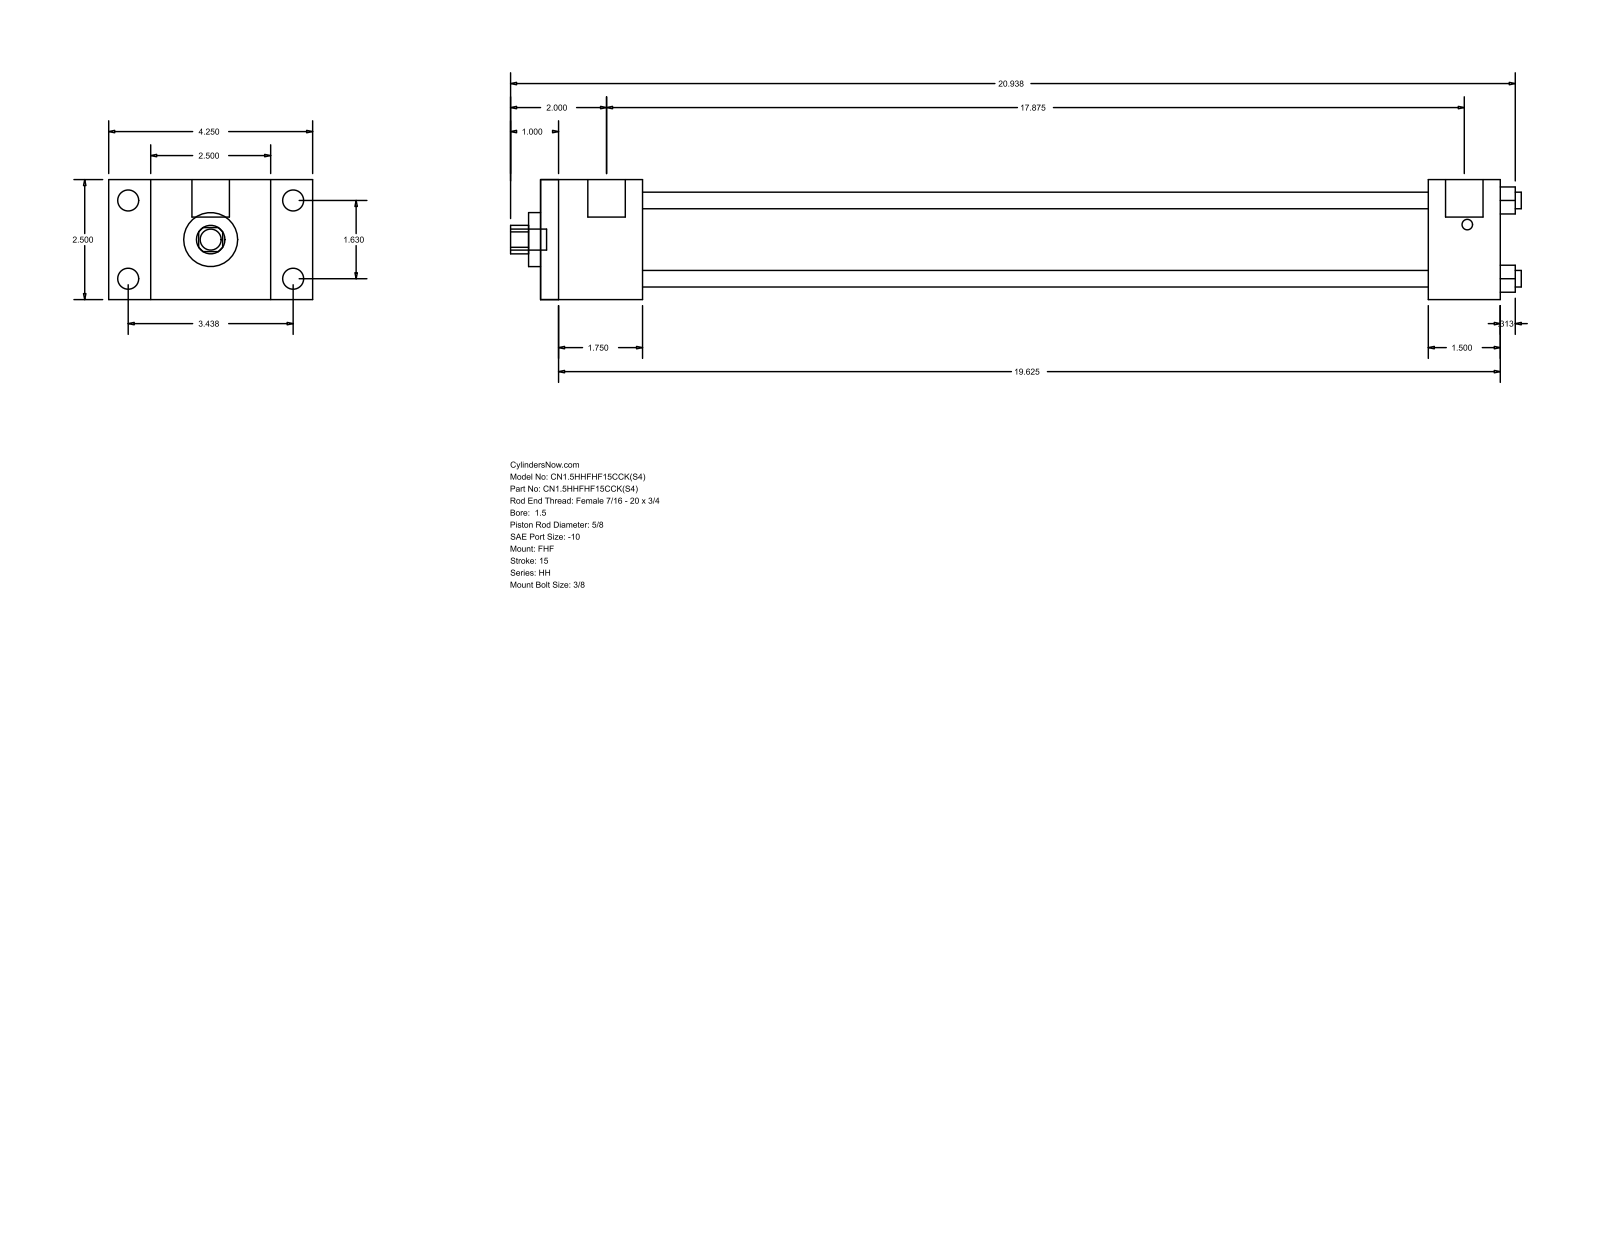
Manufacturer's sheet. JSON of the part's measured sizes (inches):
{"part_name": "HH_FHF__0150_0.625", "step_written_by": "GSSL Pune (CONFIG_CONTROL_DESIGN)", "units": "inches", "bodies": {"solids": 0, "faces": 88, "planar": 60, "cylindrical": 28, "other": 0}, "overall_size": [21.063, 4.25, 2.5], "round_holes": [[0.345, 4], [0.625, 1], [1.125, 1], [1.75, 1]], "round_bosses_or_shafts": [[0.438, 4], [0.219, 4], [0.781, 2], [0.437, 1]], "partial_cylinders_radius": [[0.297, 1]], "face_to_face_distances": [2.5, 0.875, 3.375, 2.125, 4.25, 20, 17.875, 18.5, 16.375, 1.5], "hole_center_spacings": [1.152, 1.63, 2.305]}
